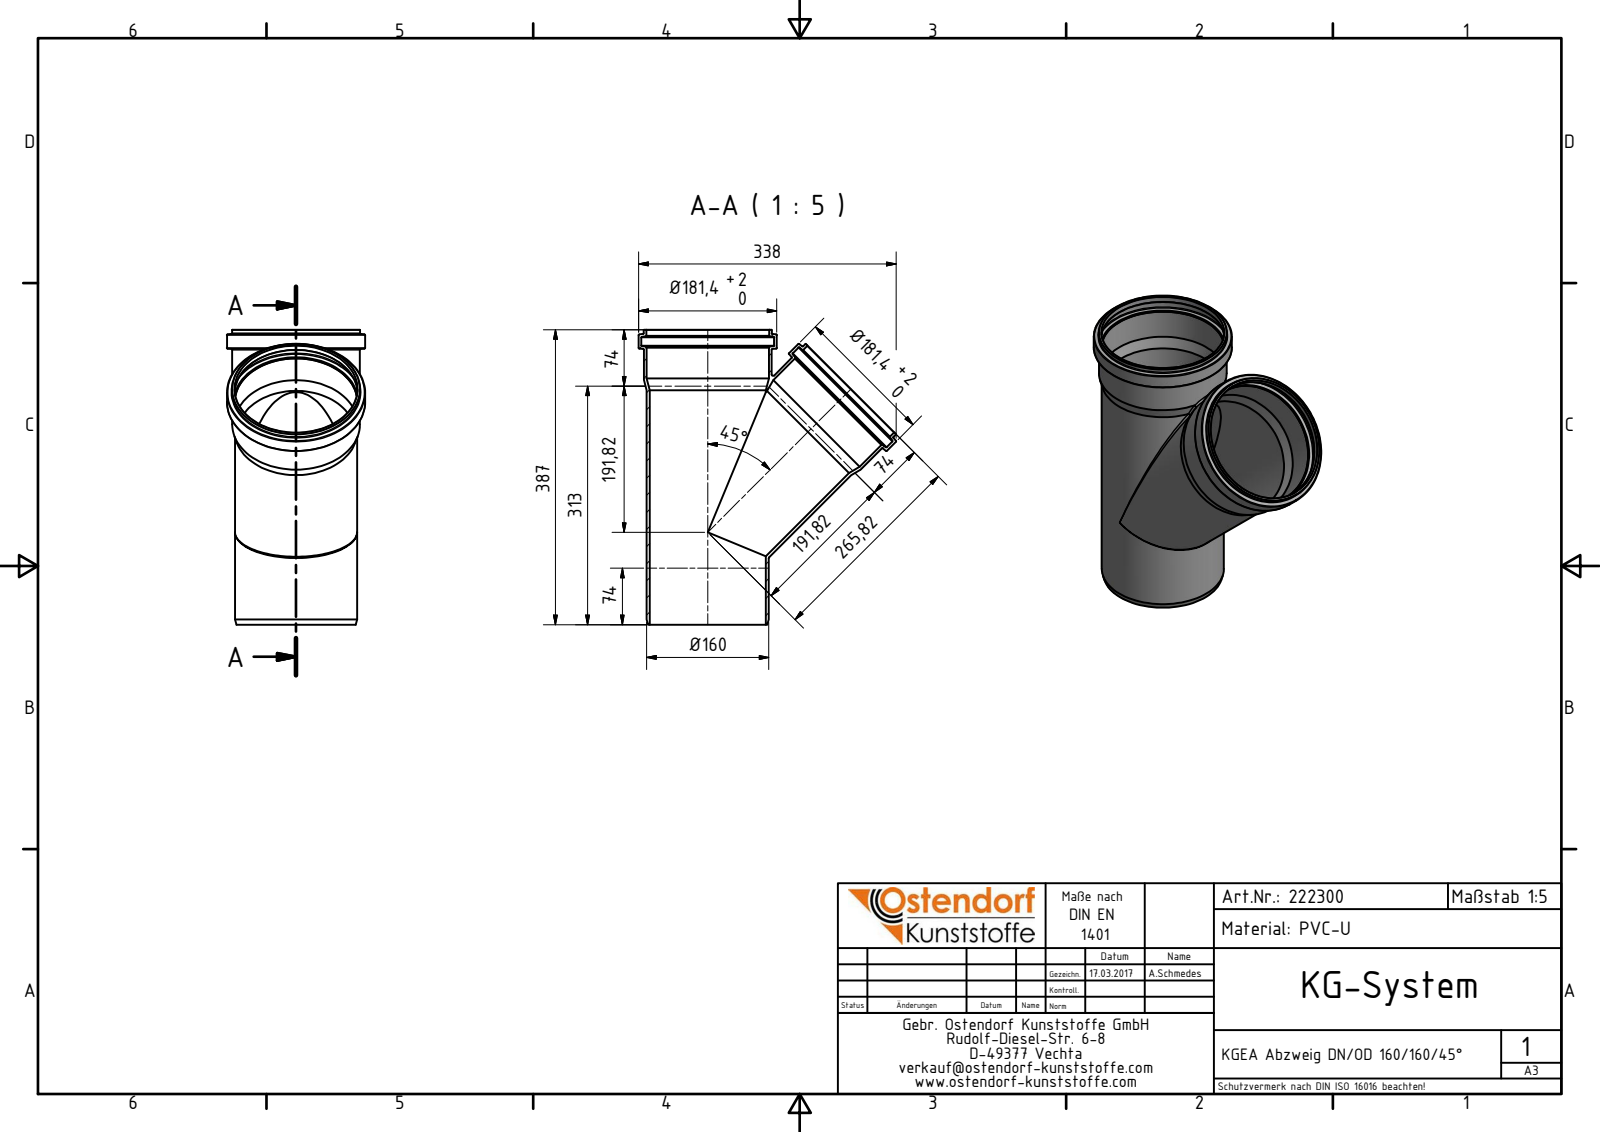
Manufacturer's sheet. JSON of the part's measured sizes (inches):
{"part_name": "222300 KGEA Abzweig DN_OD 160_160_45°", "step_written_by": "Autodesk Inventor 2016 (AUTOMOTIVE_DESIGN)", "units": "inches", "bodies": {"solids": 1, "faces": 62, "planar": 5, "cylindrical": 18, "other": 39}, "overall_size": [15.236, 13.307, 7.142], "volume_in3": 63.04, "surface_area_in2": 837.1, "round_holes": [[6.343, 3], [5.996, 2], [6.327, 2], [6.866, 2]], "round_bosses_or_shafts": [[7.142, 2], [6.618, 2], [6.602, 2], [6.311, 2]], "face_to_face_distances": [15.236, 0.929, 14.307]}
